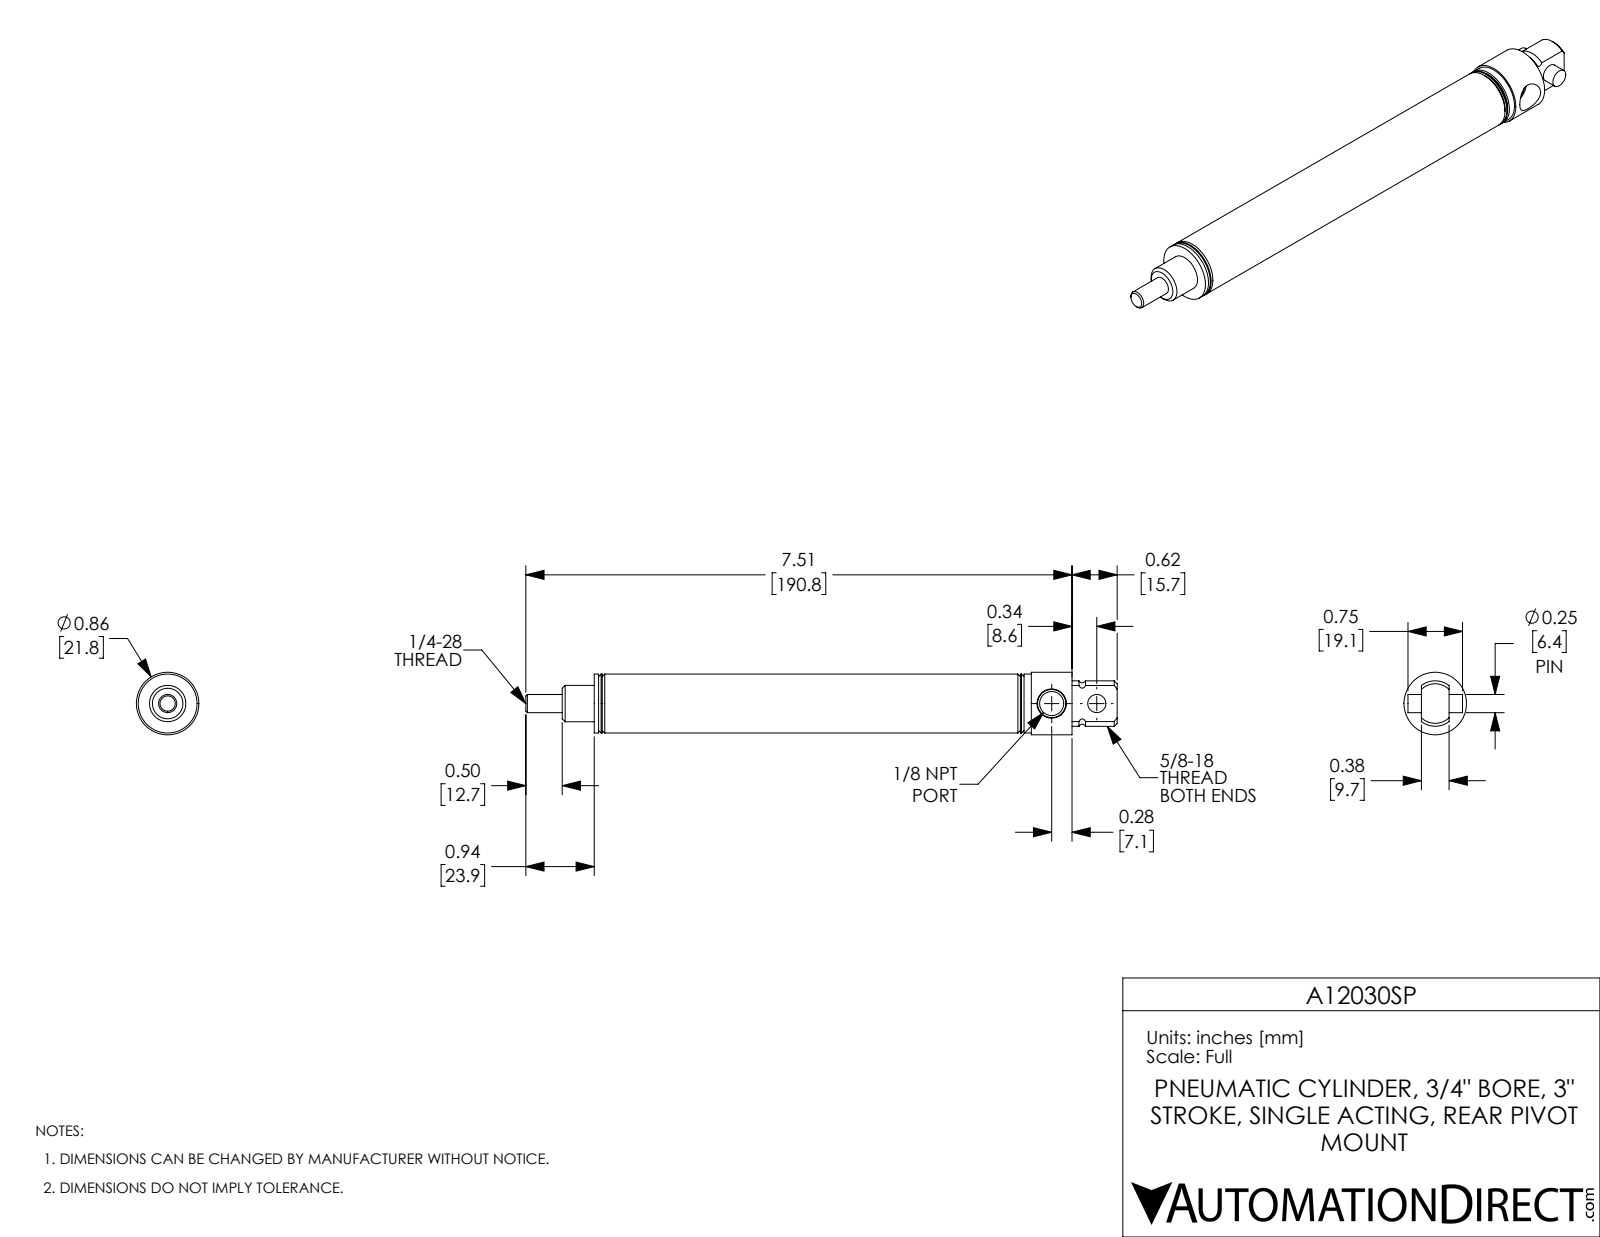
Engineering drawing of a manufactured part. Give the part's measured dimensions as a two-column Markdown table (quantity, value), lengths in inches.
| quantity | value |
| --- | --- |
| part name | A12030SP-Pin; A12030SP-Rod; A12030SP; A12030SP-MainBody |
| STEP written by | SolidWorks 2017 (AUTOMOTIVE_DESIGN) |
| units | inches |
| bodies | 3 solids, 73 faces (19 planar, 32 cylindrical, 22 other) |
| overall size | 8.13 × 0.86 × 0.86 |
| volume | 2.45 in³ |
| surface area | 38.52 in² |
| round holes (diameter × count) | 0.25 × 2, 0.332 × 1, 0.75 × 1 |
| round bosses / shafts (diameter × count) | 0.86 × 1, 0.81 × 1, 0.5 × 1 |
| partial cylindrical surfaces (radius × count) | 0.313 × 1 |
| main face-to-face distances | 1.535, 5.035, 0.5, 0.5, 3.5, 3.5, 3, 1.535, 2.035, 6.57 |
| hole center spacings | 0.62 |
